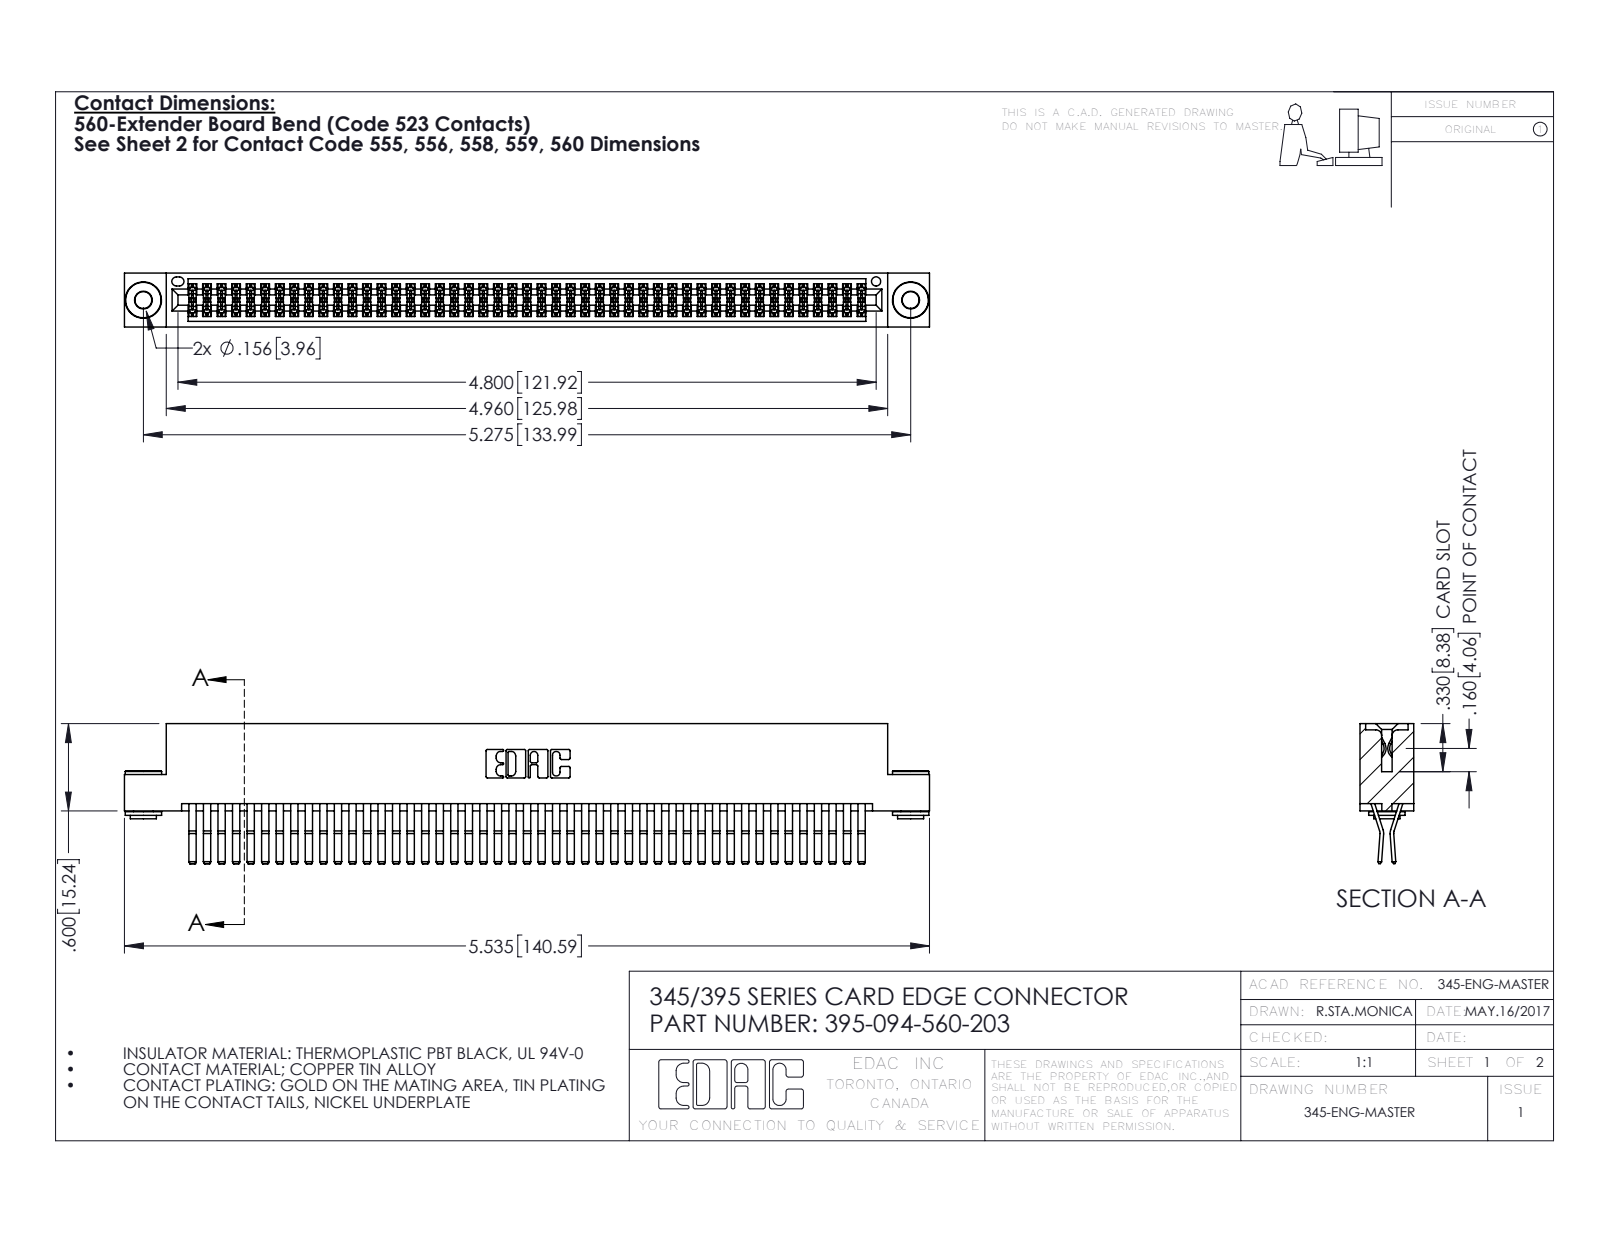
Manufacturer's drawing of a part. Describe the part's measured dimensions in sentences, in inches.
The part is named "345 Part_Flush Mounting Lugs - 0.156 Dia-TH; 395-094-560-203; 345-250-002_345-250-002-102; 345-292-001_560 Tail". Its 3-D file was written by "SolidWorks 2016 (CONFIG_CONTROL_DESIGN)". It is 97 solids with 5052 faces: 3192 planar, 1852 cylindrical and 8 other. Overall it measures 5.535 by 0.962 by 0.37 inches. Its volume is 0.875 cubic inches and its surface area 35.78 square inches. Round holes: 2 of diameter 0.116, 2 of diameter 0.156, 1 of diameter 0.064. Round bosses or shafts: 2 of diameter 0.25, 2 of diameter 0.18, 2 of diameter 0.136. Partial cylindrical surfaces (rounded edges, fillets, slot ends): 141 of radius 0.006, 22 of radius 0.01, 6 of radius 0.007, 6 of radius 0.031, 3 of radius 0.026, 2 of radius 0.01, 2 of radius 0.014, 2 of radius 0.019. The main face-to-face distances are 0.025, 0.072, 0.298, 0.2, 0.37, 0.098, 0.272, 0.225, 0.175, 0.149. The hole center spacings are 0.27, 5.039, 5.275.
